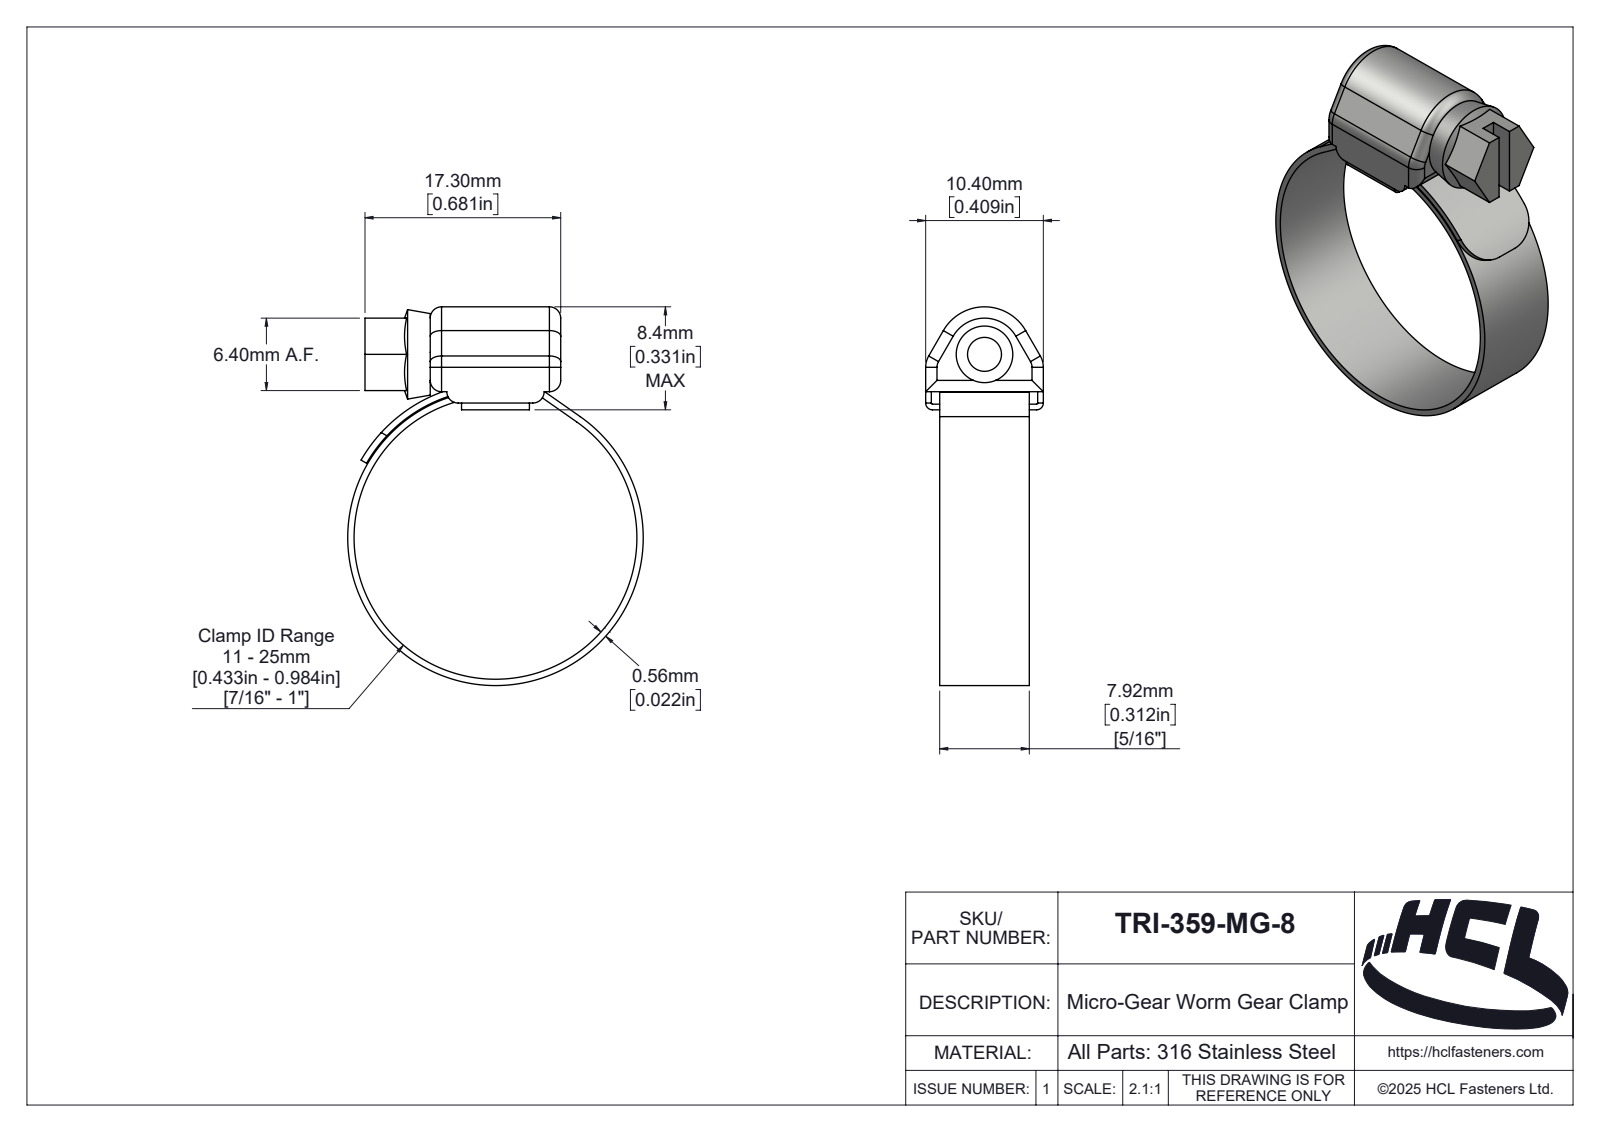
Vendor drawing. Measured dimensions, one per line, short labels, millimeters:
name: TRI-359-MG-8
written by: SolidWorks 2025 (AUTOMOTIVE_DESIGN)
unit: mm
bodies: 3 solids, 186 faces (38 planar, 87 cylindrical, 61 other)
size: 33.46 × 26.12 × 10.4
volume: 1 361 mm³; area: 2 772 mm²
holes: 1× ⌀5, 1× ⌀25
bosses: 1× ⌀26.12
rounds: 12× R1, 3× R2, 2× R0.1, 2× R0.6, 2× R3, 1× R0.25, 1× R1.01, 1× R1.26
face distances: 1.1, 0.5, 1.24, 9.16, 1.6, 7.92, 6.2, 0.56, 10.4, 5.76
